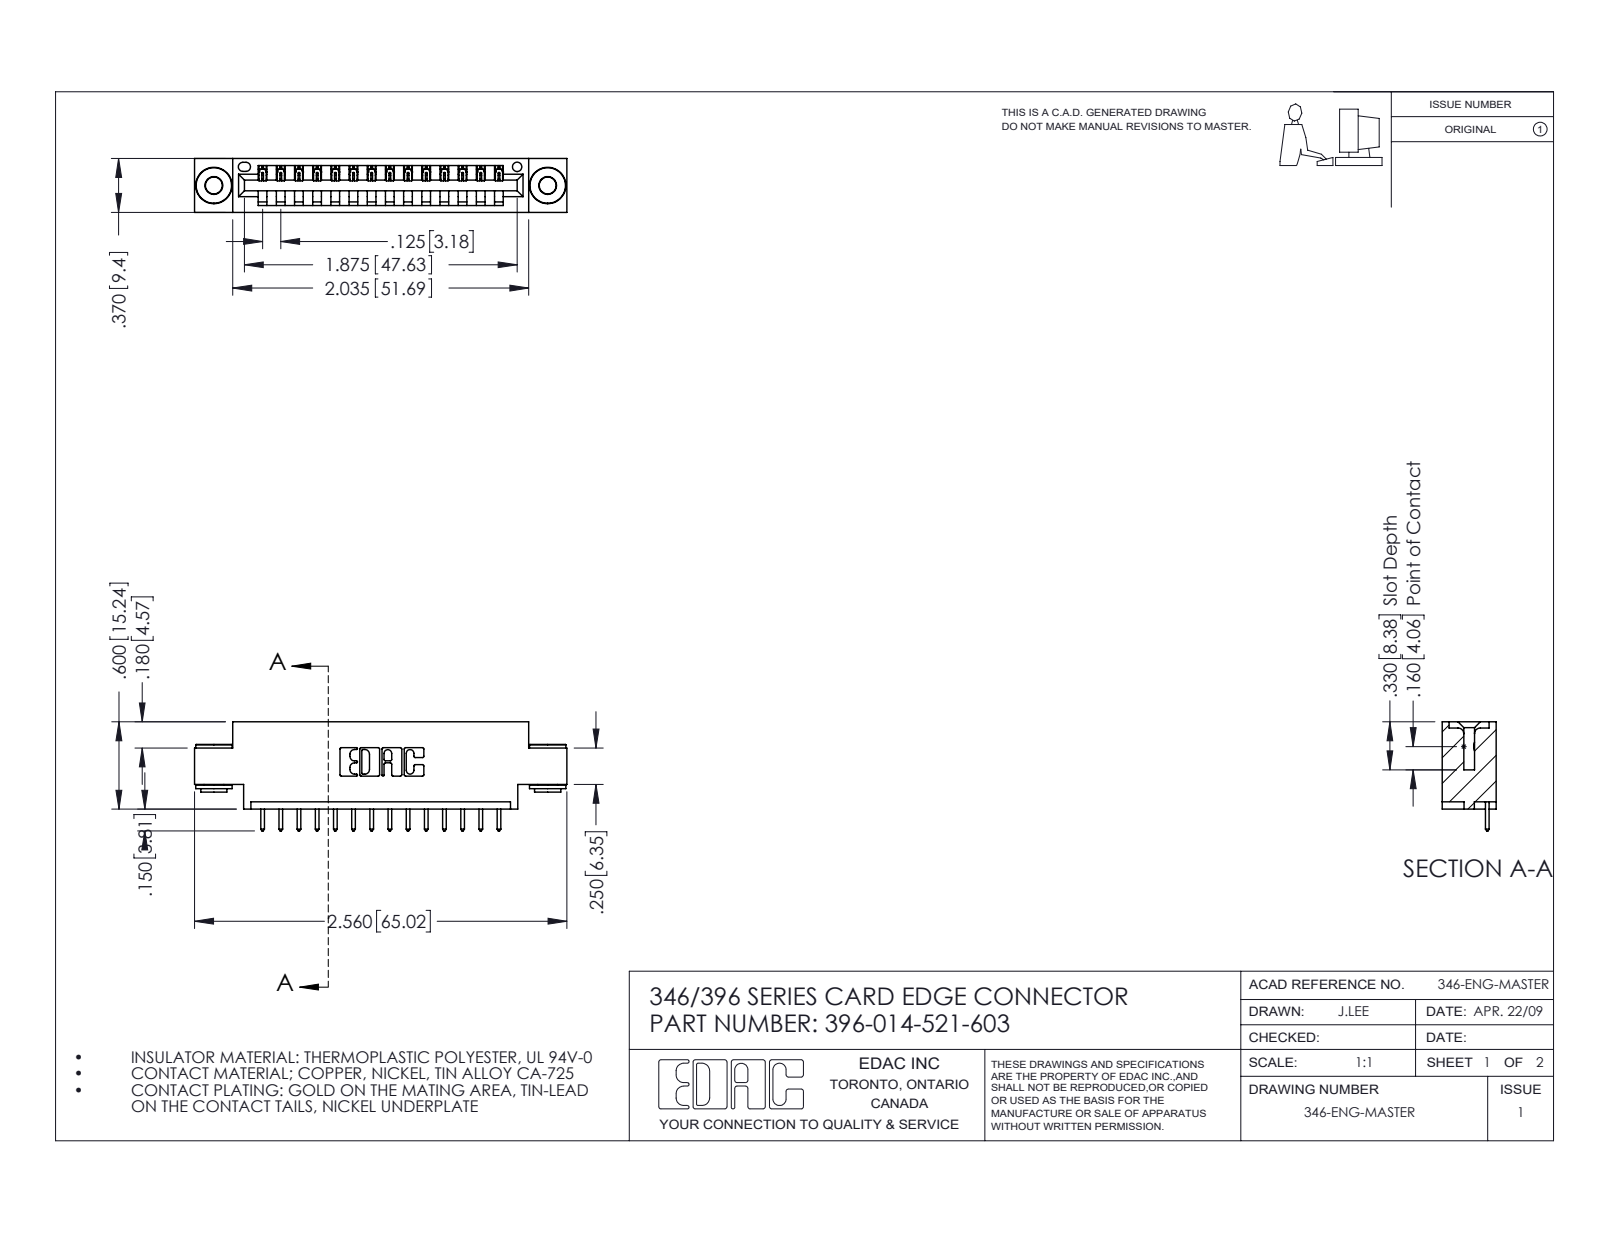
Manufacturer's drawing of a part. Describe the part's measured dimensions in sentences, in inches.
The part is named "345-250-002_345-250-002-102; 345-292-001_345-293-121; 346 Part_0.170 Offset - 0.156 Dia-TH; 396-014-521-603". Its 3-D file was written by "SolidWorks 2016 (CONFIG_CONTROL_DESIGN)". It is 17 solids with 976 faces: 650 planar, 318 cylindrical and 8 other. Overall it measures 2.56 by 0.75 by 0.37 inches. Its volume is 0.357 cubic inches and its surface area 11.22 square inches. Round holes: 2 of diameter 0.116, 2 of diameter 0.156, 1 of diameter 0.064. Round bosses or shafts: 2 of diameter 0.25, 2 of diameter 0.18, 2 of diameter 0.136. Partial cylindrical surfaces (rounded edges, fillets, slot ends): 28 of radius 0.006, 28 of radius 0.01, 22 of radius 0.01, 6 of radius 0.007, 6 of radius 0.031, 3 of radius 0.026, 2 of radius 0.031, 2 of radius 0.04. The main face-to-face distances are 0.37, 0.048, 0.322, 0.25, 0.025, 0.072, 0.298, 0.148, 0.222, 0.1. The hole center spacings are 0.246, 2.089, 2.295.
